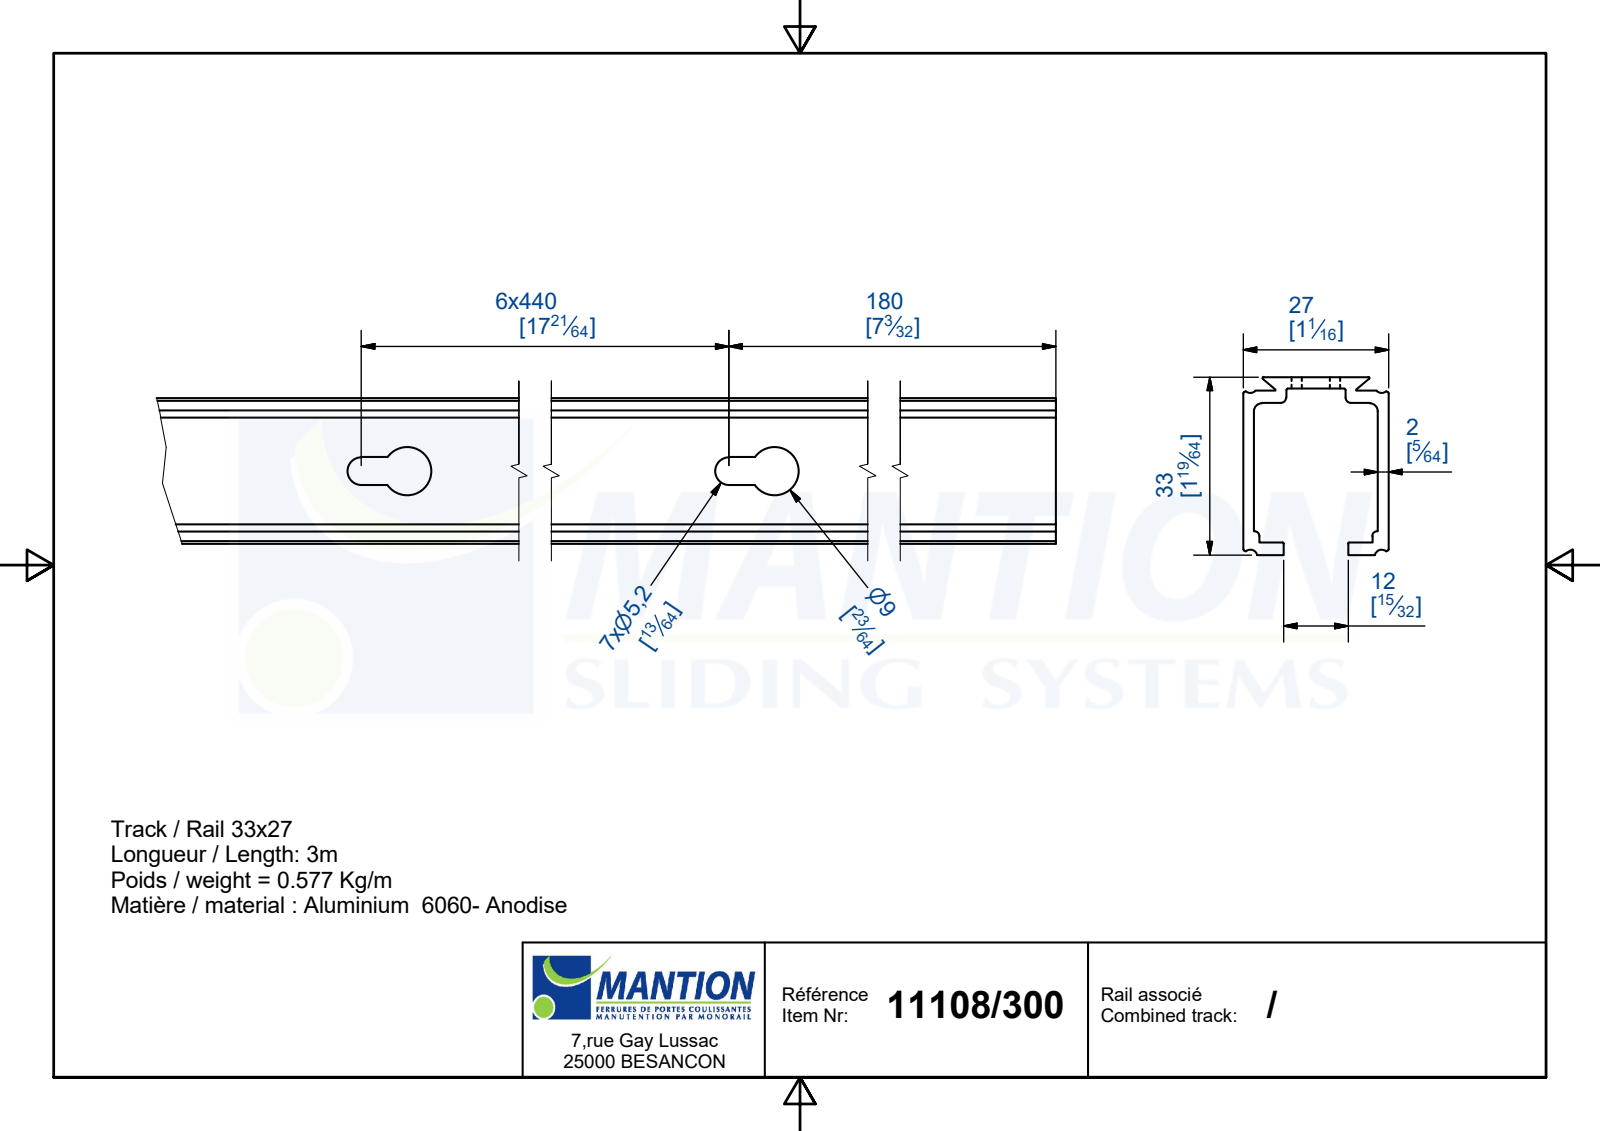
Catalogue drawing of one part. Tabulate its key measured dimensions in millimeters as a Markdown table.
| quantity | value |
| --- | --- |
| part name | 11108 |
| STEP written by | Autodesk Inventor 2019 (AUTOMOTIVE_DESIGN) |
| units | millimeters |
| bodies | 1 solid, 80 faces (46 planar, 34 cylindrical, 0 other) |
| overall size | 3000 × 33 × 27 |
| volume | 638 471 mm³ |
| surface area | 618 668 mm² |
| round holes (diameter × count) | 9 × 7 |
| partial cylindrical surfaces (radius × count) | 2.6 × 7, 0.3 × 6, 0.2 × 4, 1.3 × 4, 0.9 × 2, 1 × 2, 1.5 × 2 |
| main face-to-face distances | 2, 25, 27, 23, 2.3, 28.2, 2.1, 30.9, 33, 28.6 |
| hole center spacings | 440, 880, 1320, 1760, 2200, 2640 |
